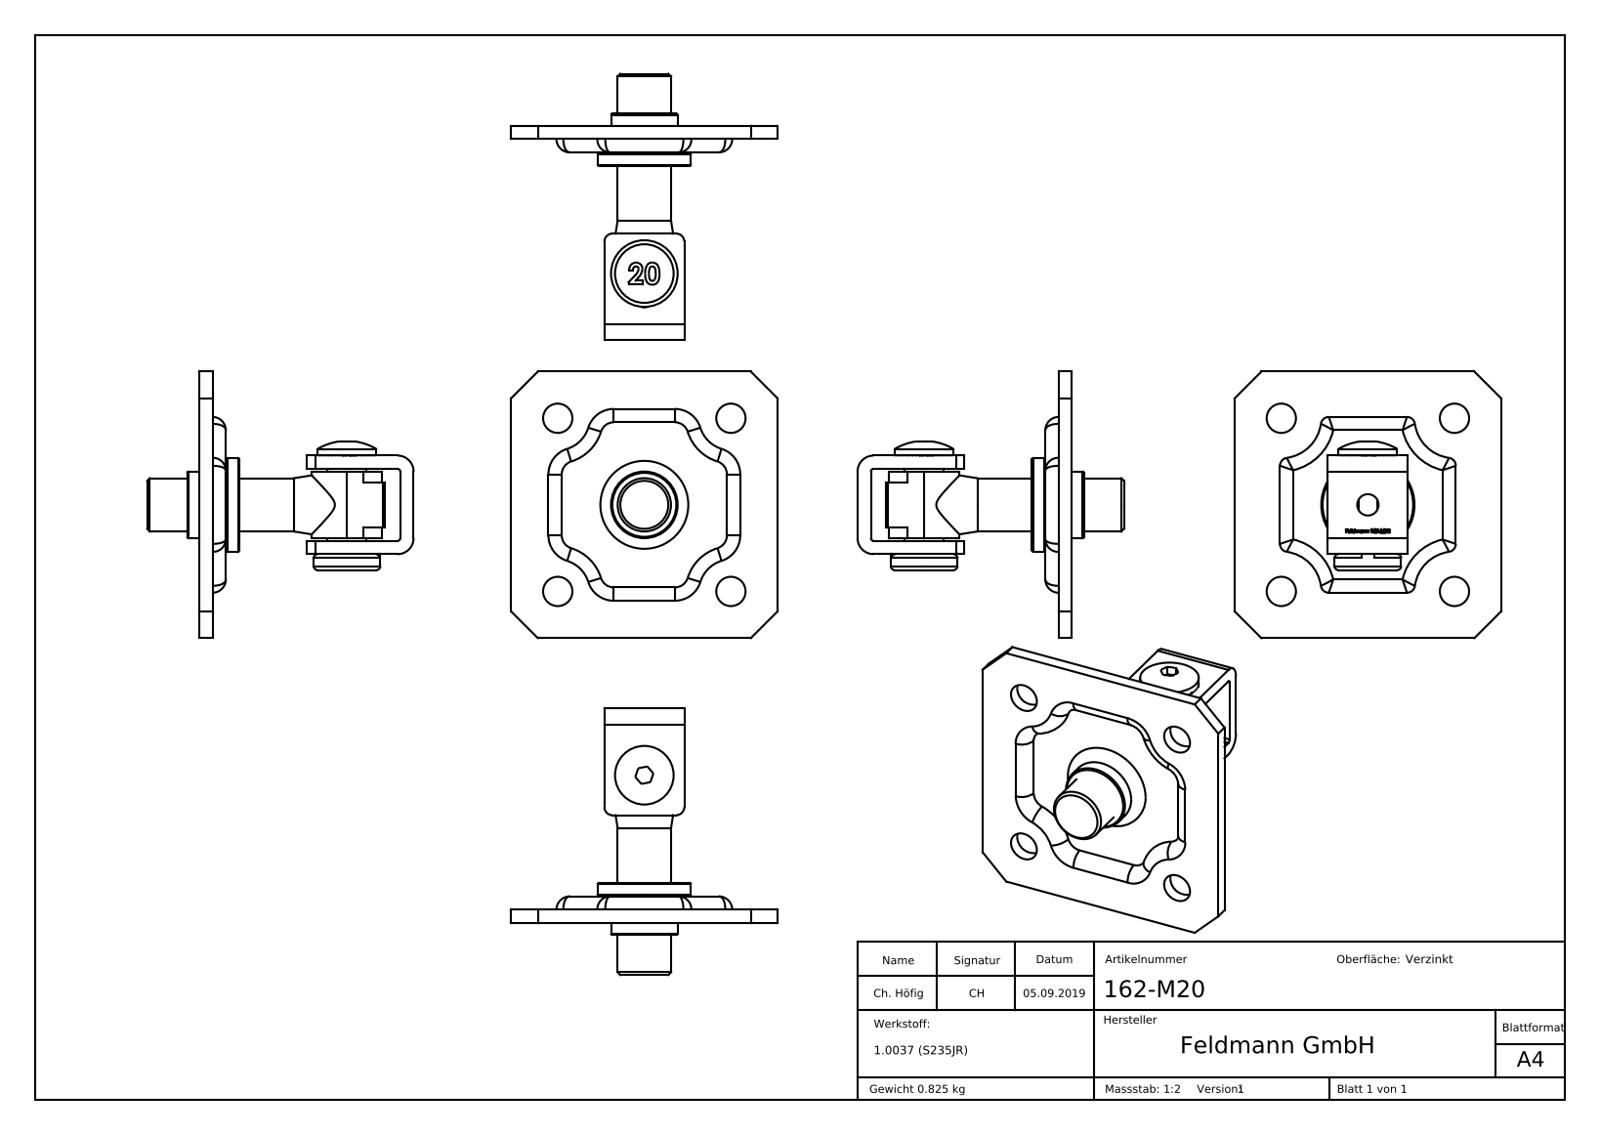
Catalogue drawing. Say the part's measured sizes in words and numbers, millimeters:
The part is named "162-M20; 162-MXX Teil4_162-M20 Teil4; 162-MXX Teil3_162-M20 Teil3; 162-MXX Teil5_162-M20 Teil4 (+2 more)". Its 3-D file was written by "SolidWorks 2015 (CONFIG_CONTROL_DESIGN)". It is 5 solids with 531 faces: 319 planar, 64 cylindrical and 148 other. Overall it measures 100 by 100 by 100 millimeters. Its volume is 105 827 cubic millimeters and its surface area 44 903 square millimeters. Round holes: 5 of diameter 11, 1 of diameter 8, 1 of diameter 8.5, 1 of diameter 14.9, 1 of diameter 15, 1 of diameter 17.5. Round bosses or shafts: 2 of diameter 25, 1 of diameter 35, 1 of diameter 33, 1 of diameter 26.5, 1 of diameter 22, 1 of diameter 20, 1 of diameter 14.5, 1 of diameter 10. Partial cylindrical surfaces (rounded edges, fillets, slot ends): 8 of radius 5, 2 of radius 1, 2 of radius 3, 2 of radius 6, 2 of radius 15, 1 of radius 3.1, 1 of radius 10. The main face-to-face distances are 5, 10, 32, 70.5, 75.5, 37, 6, 100, 35, 27. The hole center spacings are 45.96, 65, 91.92.
